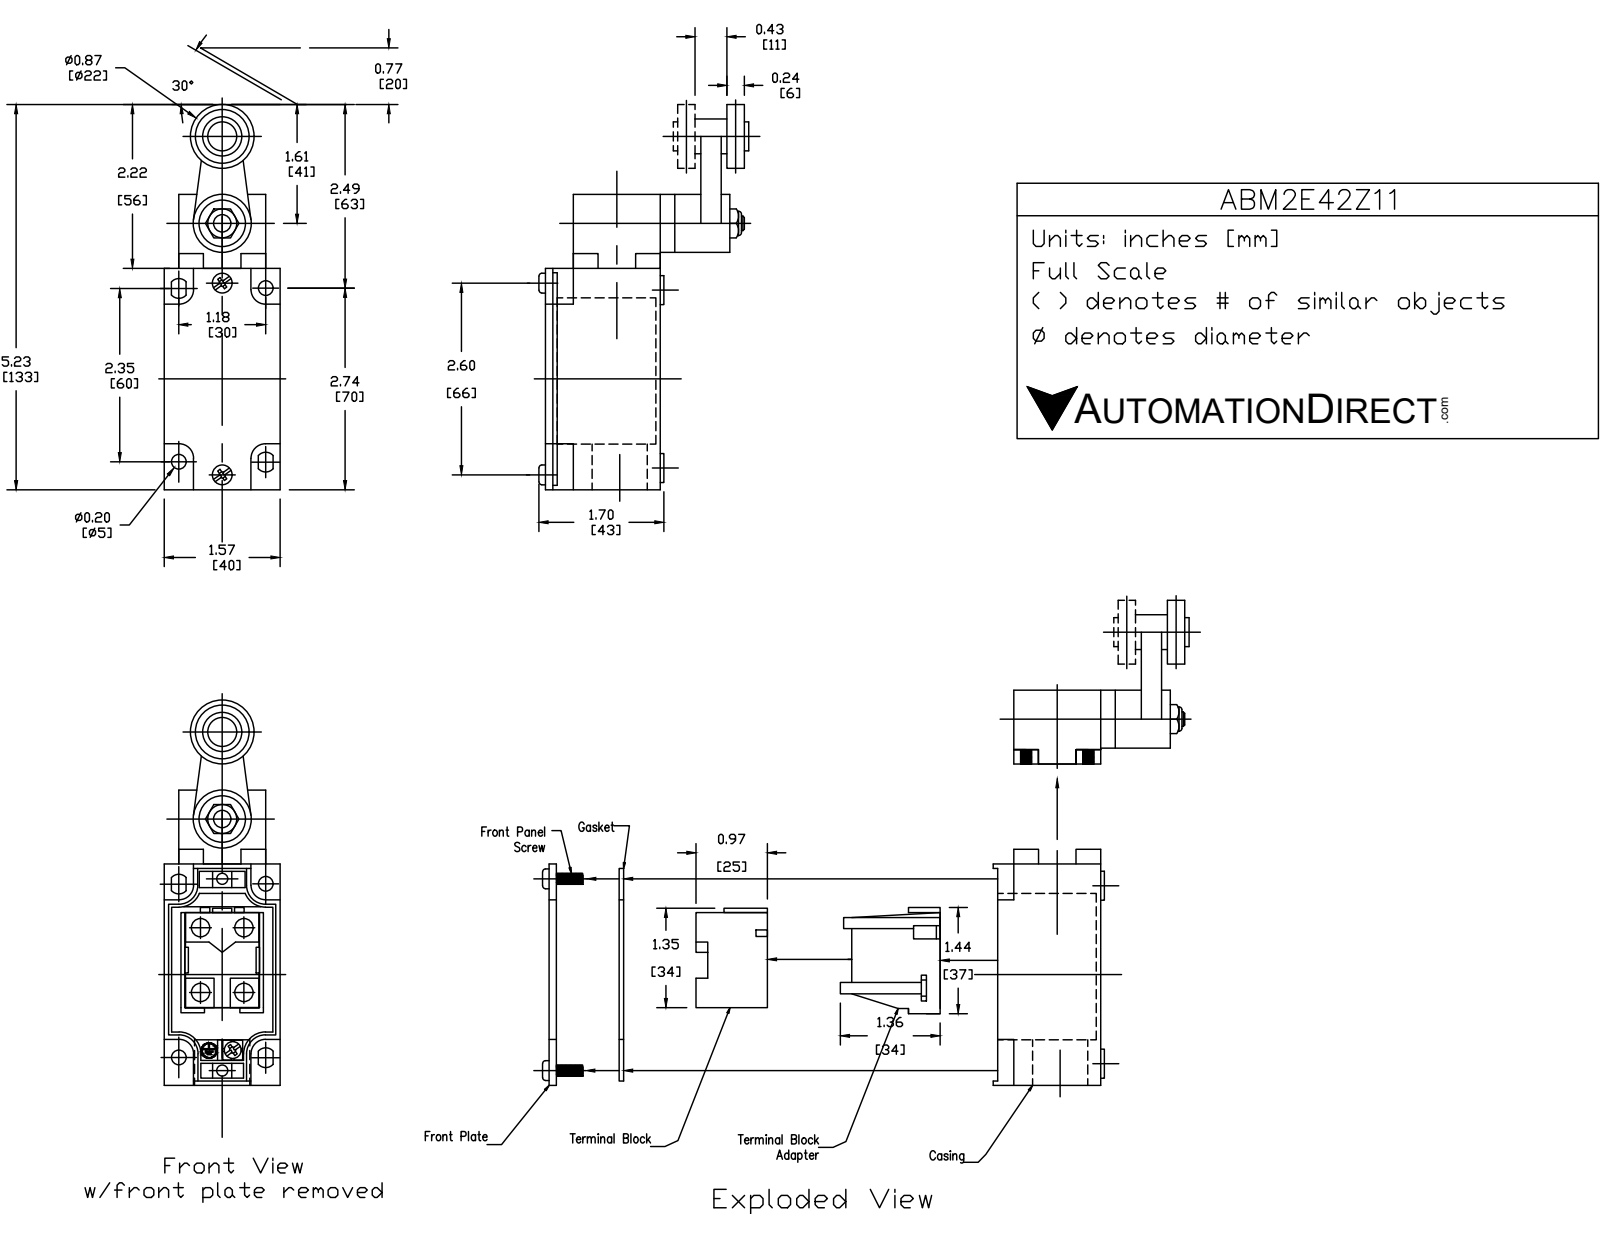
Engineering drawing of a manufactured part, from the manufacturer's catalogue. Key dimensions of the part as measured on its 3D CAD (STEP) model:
Part name (STEP PRODUCT): ABM2E42Z11
STEP written by: SolidWorks 2017 (AUTOMOTIVE_DESIGN)
Units: inches
Bodies: 3 solids, 223 faces (90 planar, 92 cylindrical, 41 other)
Overall size (bounding box): 5.236 × 2.4 × 1.575
Volume: 8.783 in³ · Surface area: 44.36 in²
Round holes (diameter × count): ⌀0.205 ×2, ⌀0.551 ×1, ⌀0.669 ×1, ⌀0.748 ×1
Round bosses / shafts (diameter × count): ⌀0.394 ×6, ⌀0.276 ×3, ⌀0.866 ×1, ⌀0.787 ×1, ⌀0.453 ×1, ⌀0.236 ×1
Partial cylindrical surfaces — rounded edges, fillets, slot ends (radius × count): R0.059 ×16, R0.039 ×4, R0.197 ×4, R0.128 ×2, R0.236 ×1, R0.453 ×1, R0.472 ×1
Main face-to-face distances: 1.575, 1.555, 0.197, 1.181, 1.378, 3.012, 0.984, 0.374, 0.02, 4.016
Hole centre spacings: 1.048, 2.641, 3.282
